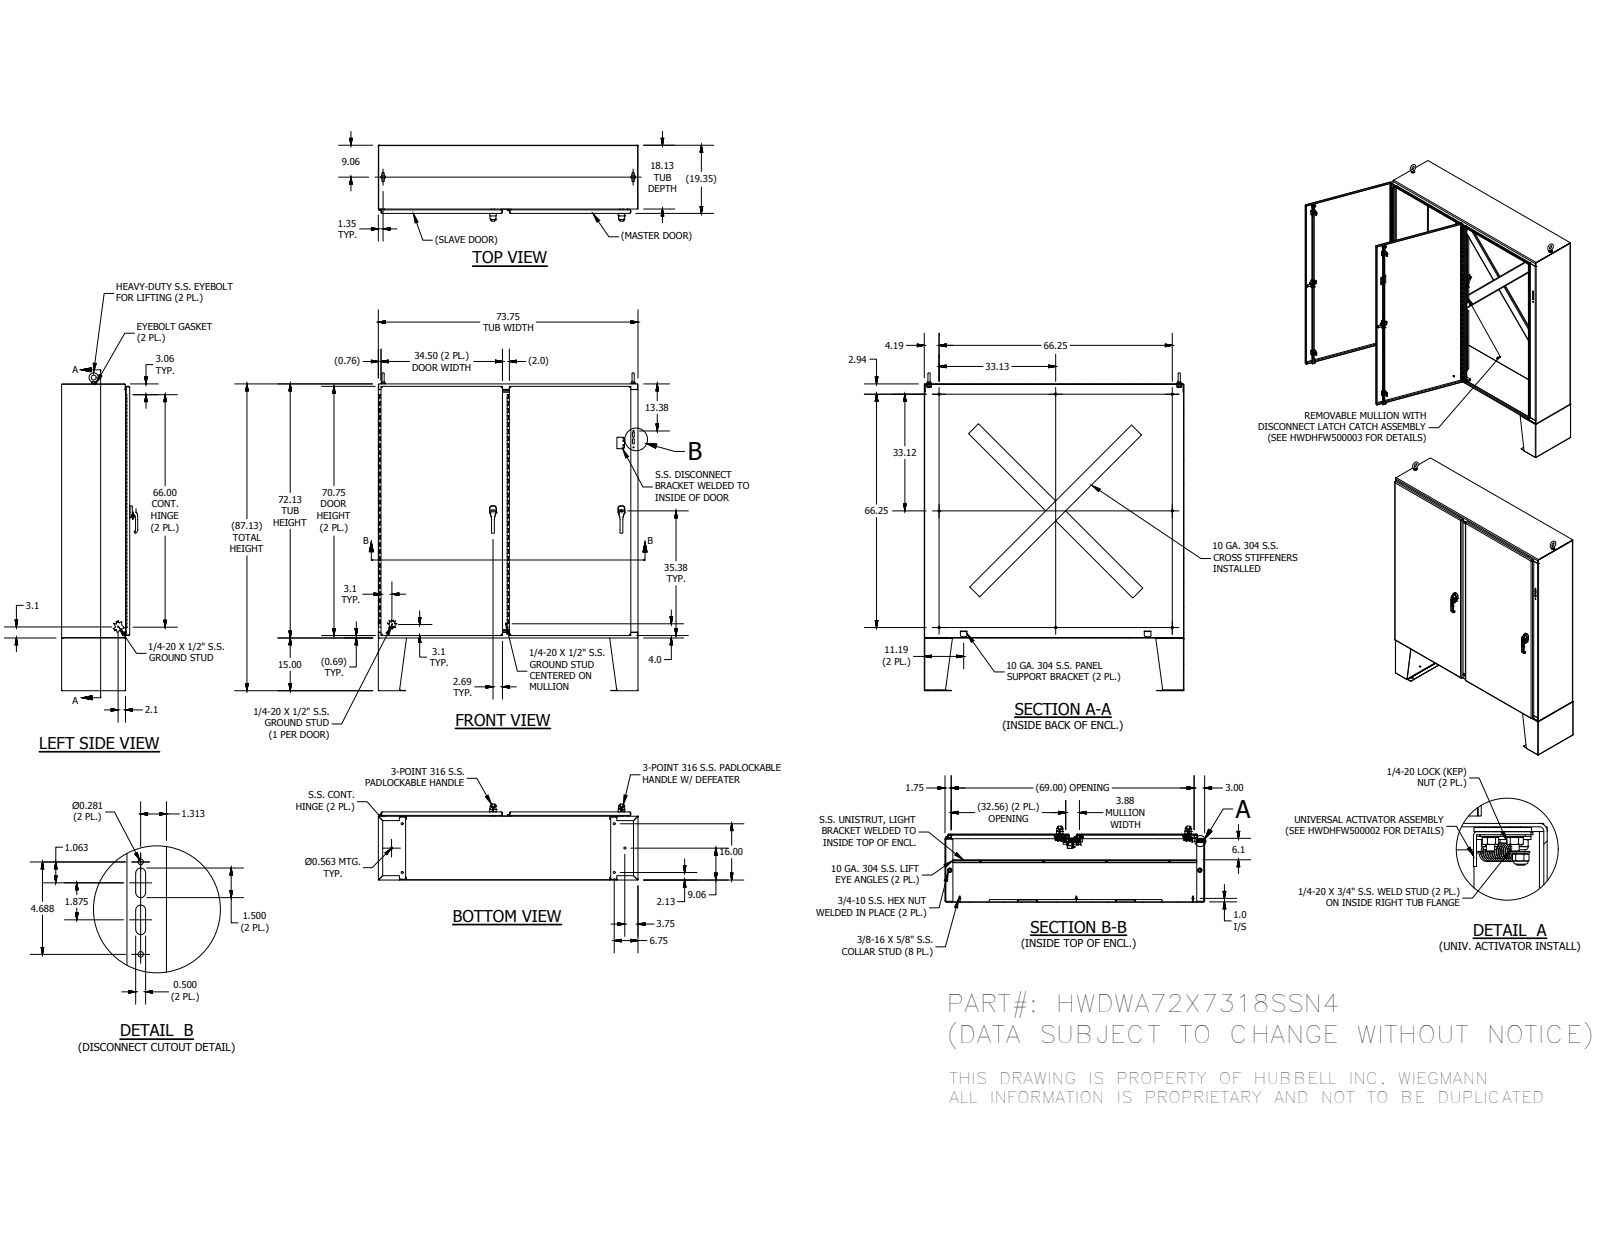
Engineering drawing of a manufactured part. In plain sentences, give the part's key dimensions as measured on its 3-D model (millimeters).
The part is named "WA72X7318SSN4BLR; WAX7318SSN4TOP; WAX7318SSN4BTM; HFW332010S (+8 more)". Its 3-D file was written by "Autodesk Inventor 2016 (AUTOMOTIVE_DESIGN)". It is 220 solids with 9190 faces: 4286 planar, 3104 cylindrical and 1800 other. Overall it measures 2292.29 by 1873.25 by 548.55 millimeters. Its volume is 35 340 000 cubic millimeters and its surface area 26 750 000 square millimeters. Round holes: 18 of diameter 9.52, 18 of diameter 14.29, 17 of diameter 6.35, 9 of diameter 4.76, 8 of diameter 4.83, 8 of diameter 4.98, 8 of diameter 6.65, 8 of diameter 7.33, 8 of diameter 8.51, 8 of diameter 9.65, 6 of diameter 3.96, 6 of diameter 5.4. Round bosses or shafts: 20 of diameter 6.35, 18 of diameter 8.38, 13 of diameter 15.88, 12 of diameter 8.56, 11 of diameter 9.52, 9 of diameter 14.29, 8 of diameter 7.11, 6 of diameter 25.4. Partial cylindrical surfaces (rounded edges, fillets, slot ends): 359 of radius 0.5, 221 of radius 0.3, 192 of radius 0.51, 55 of radius 3.17, 42 of radius 0.47, 28 of radius 1.27, 28 of radius 2, 23 of radius 6.35. The main face-to-face distances are 2.64, 488.79, 486.15, 491.43, 1829.34, 1870.6, 1826.7, 1831.98, 1867.96, 457.73. The hole center spacings are 9.65, 19.31, 30.36, 127, 173.87, 189.72, 425.45, 444.
